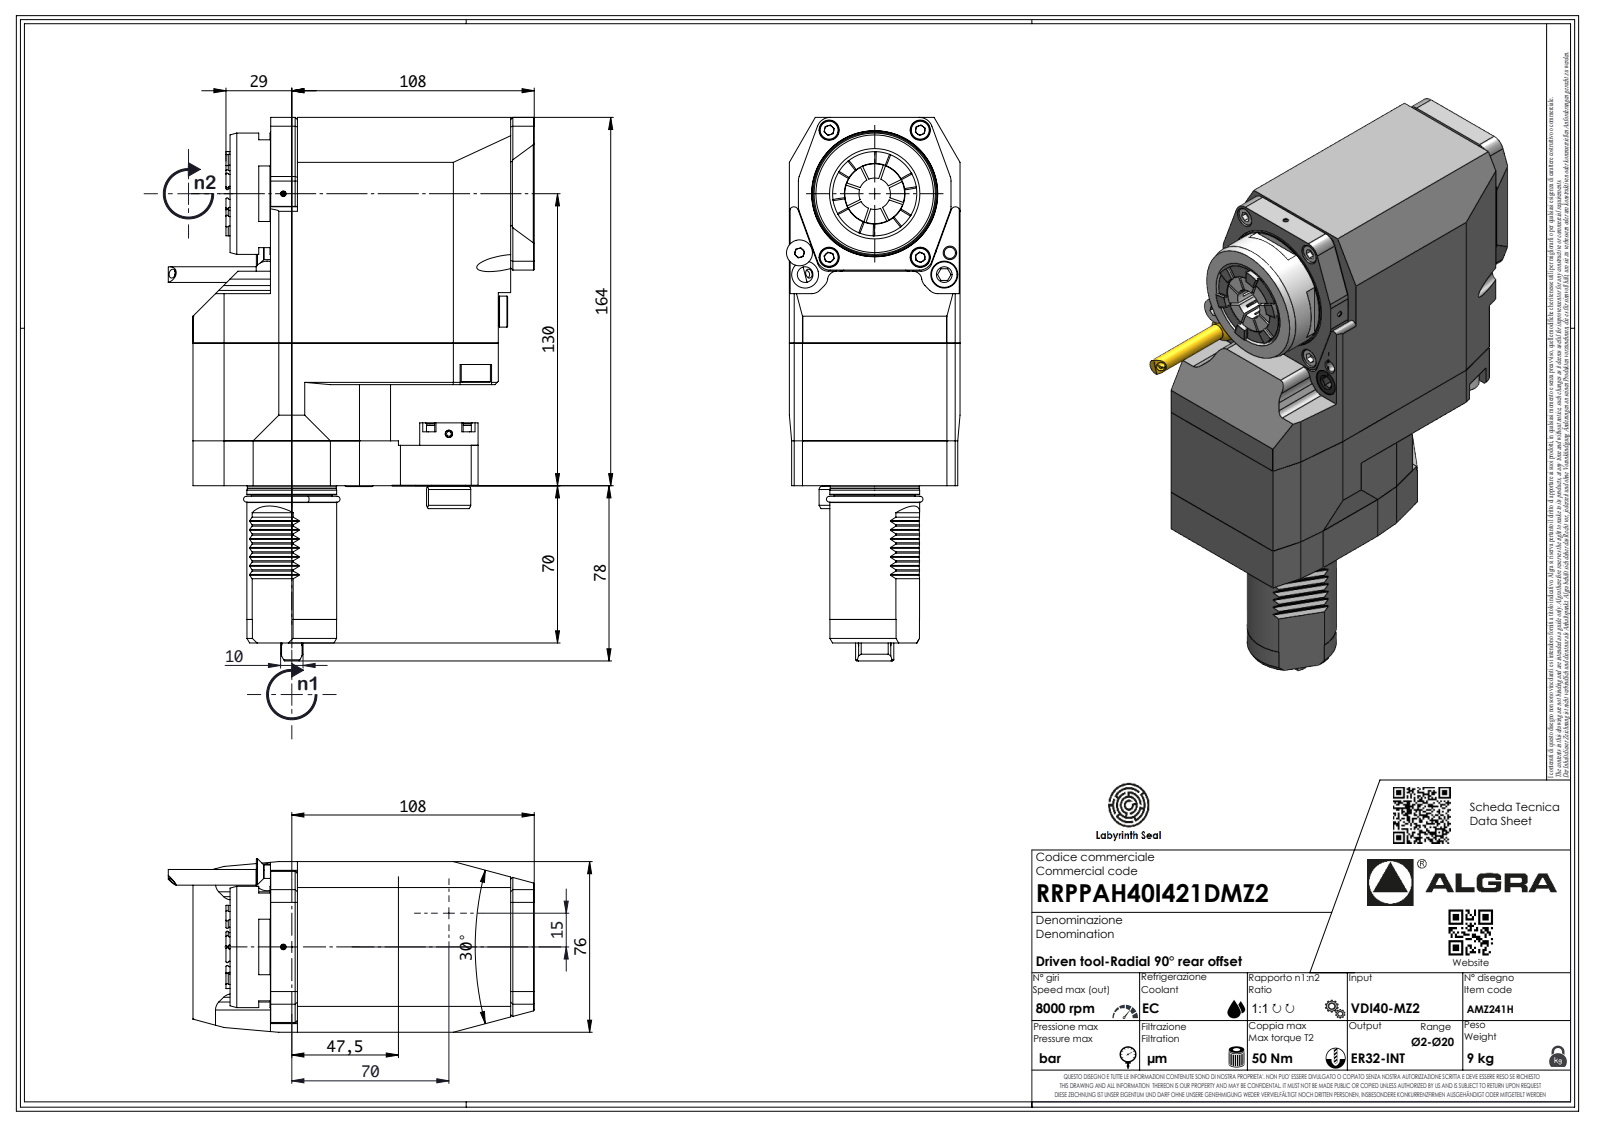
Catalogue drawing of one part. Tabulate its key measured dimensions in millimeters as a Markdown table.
| quantity | value |
| --- | --- |
| part name | RRPPAH40I421DMZ2 |
| STEP written by | SolidWorks 2023 (AUTOMOTIVE_DESIGN) |
| units | millimeters |
| bodies | 2 solids, 599 faces (418 planar, 86 cylindrical, 95 other) |
| overall size | 242 × 163.5 × 76 |
| volume | 1 503 000 mm³ |
| surface area | 103 029 mm² |
| round holes (diameter × count) | 5 × 2, 2.1 × 1, 4 × 1, 6 × 1 |
| round bosses / shafts (diameter × count) | 54 × 1, 40 × 1, 39.9 × 1, 39.6 × 1, 36 × 1, 26 × 1, 20 × 1, 15 × 1 |
| partial cylindrical surfaces (radius × count) | 6 × 10, 0.3 × 7, 0.33 × 7, 0.52 × 7, 3.7 × 7, 5 × 6, 3 × 4, 2 × 3 |
| main face-to-face distances | 76, 164, 136, 16.5, 45, 119, 152.5, 88, 119.5, 68 |
